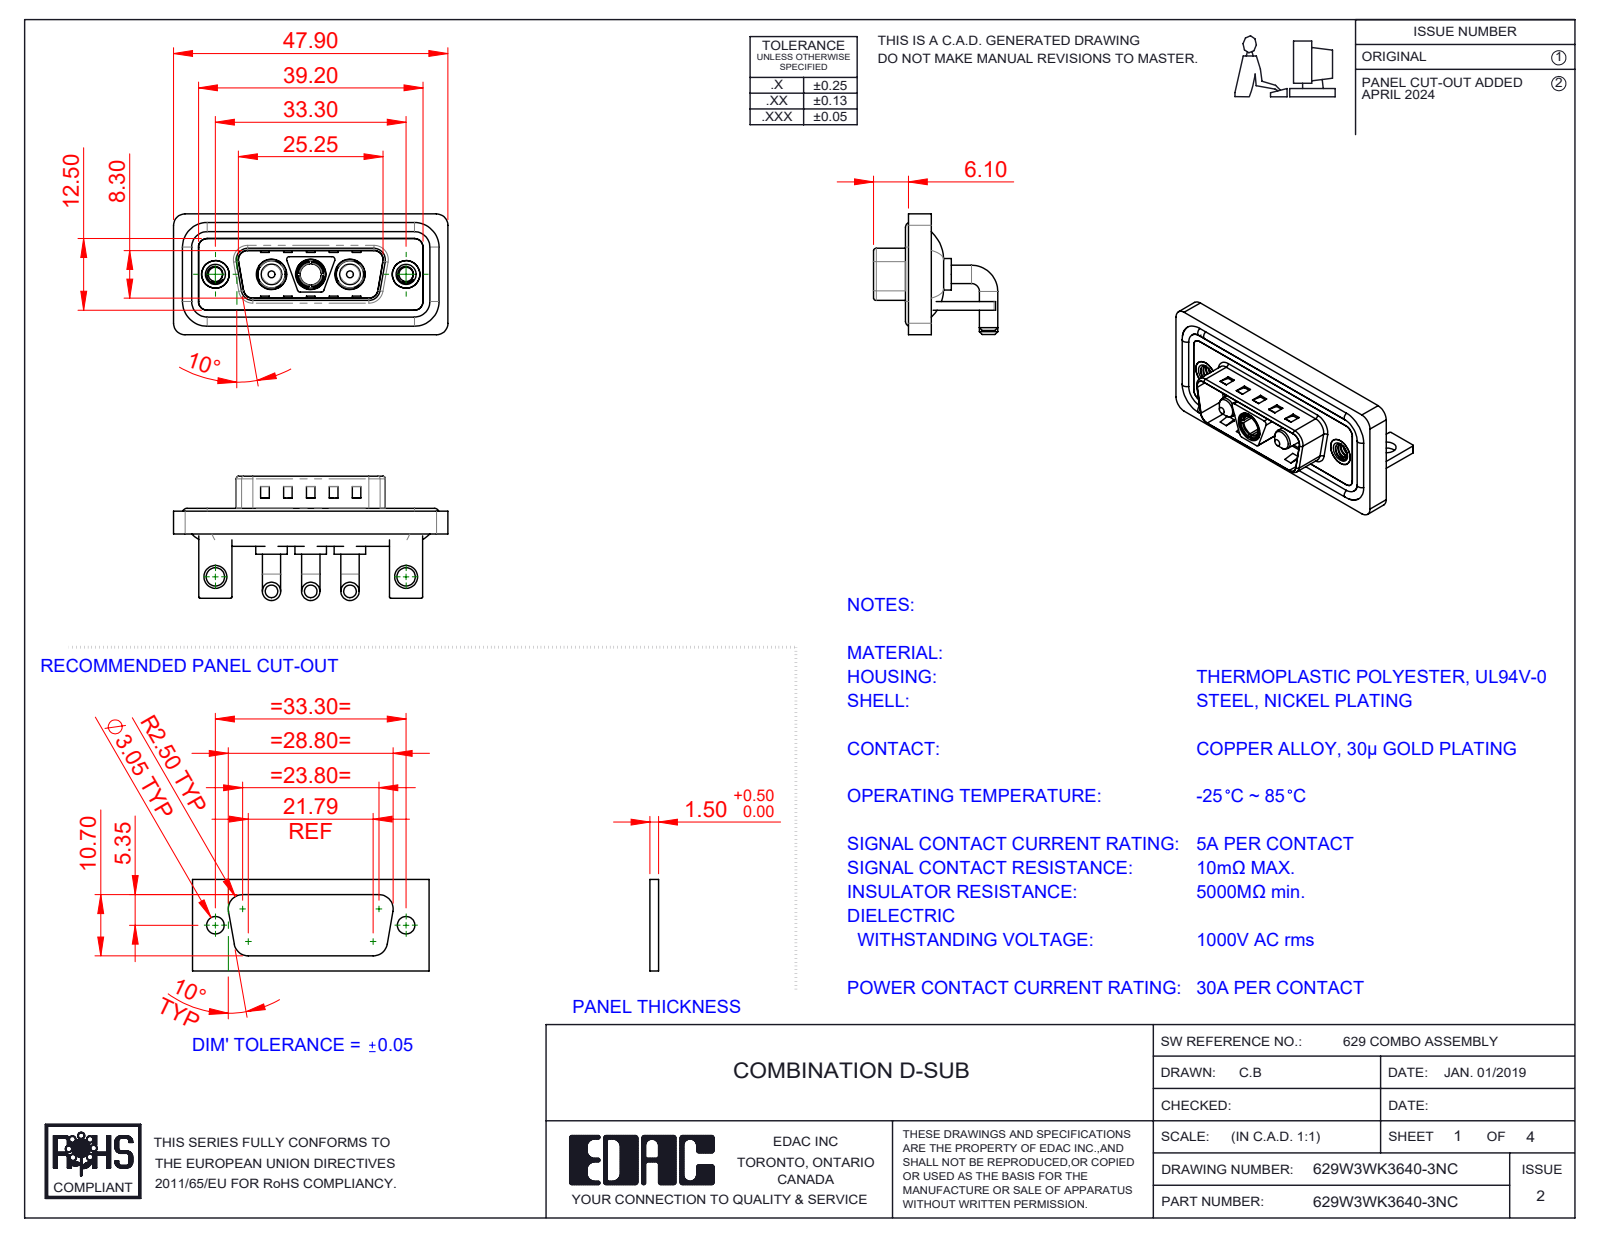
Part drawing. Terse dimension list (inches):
name: Power Pin_30A RA; 629W3WK3640-3NC; 629Combo Housing_3WK3; 629Combo Threaded Rivet_B (+5 more)
written by: SolidWorks 2023 (CONFIG_CONTROL_DESIGN)
unit: in
bodies: 15 solids, 659 faces (251 planar, 274 cylindrical, 134 other)
size: 1.886 × 0.854 × 0.831
volume: 0.381 in³; area: 15.59 in²
holes: 3× ⌀0.191, 3× ⌀0.209, 2× ⌀0.098, 2× ⌀0.126, 2× ⌀0.157, 2× ⌀0.189, 2× ⌀0.197, 1× ⌀0.146
bosses: 6× ⌀0.126, 4× ⌀0.063, 3× ⌀0.217, 3× ⌀0.205, 3× ⌀0.187, 3× ⌀0.148, 2× ⌀0.193, 2× ⌀0.142
rounds: 21× R0.079, 18× R0.059, 16× R0.01, 13× R0.02, 8× R0.063, 4× R0.024, 4× R0.026, 4× R0.035
face distances: 0.016, 0.059, 0.031, 0.114, 0.043, 0.083, 0.146, 0.063, 0.047, 0.177
hole spacings: 0.27, 0.386, 0.656, 0.925, 1.311, 0.539
